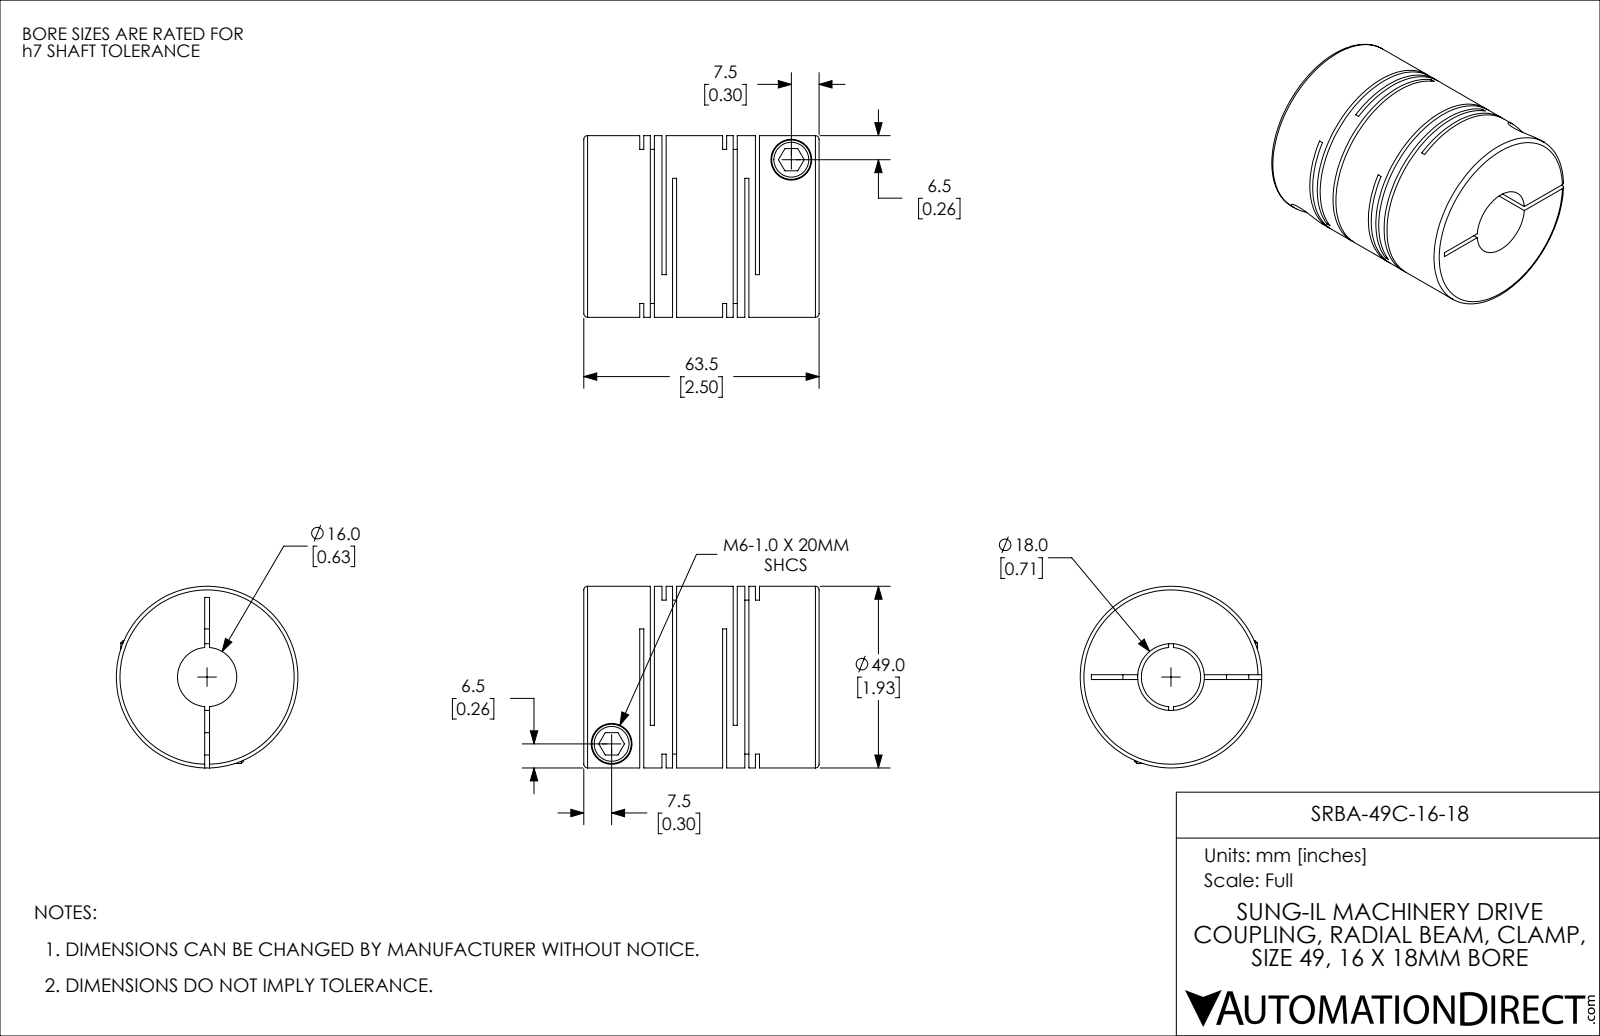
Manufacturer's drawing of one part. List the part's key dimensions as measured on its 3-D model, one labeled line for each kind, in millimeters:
Part name (STEP PRODUCT): SRBA-49C-16-18
STEP written by: SolidWorks 2021 (CONFIG_CONTROL_DESIGN)
Units: millimetres
Bodies: 1 solid, 114 faces (60 planar, 42 cylindrical, 12 other)
Overall size (bounding box): 63.5 × 49 × 49
Volume: 90 181 mm³ · Surface area: 38 881 mm²
Round holes (diameter × count): ⌀6 ×2, ⌀11 ×2, ⌀16 ×1, ⌀18 ×1
Round bosses / shafts (diameter × count): ⌀10.6 ×2, ⌀49 ×1
Main face-to-face distances: 6, 1.1, 2.85, 22.35, 4.9, 21.25, 3.15, 19.5, 16.35, 1.75
